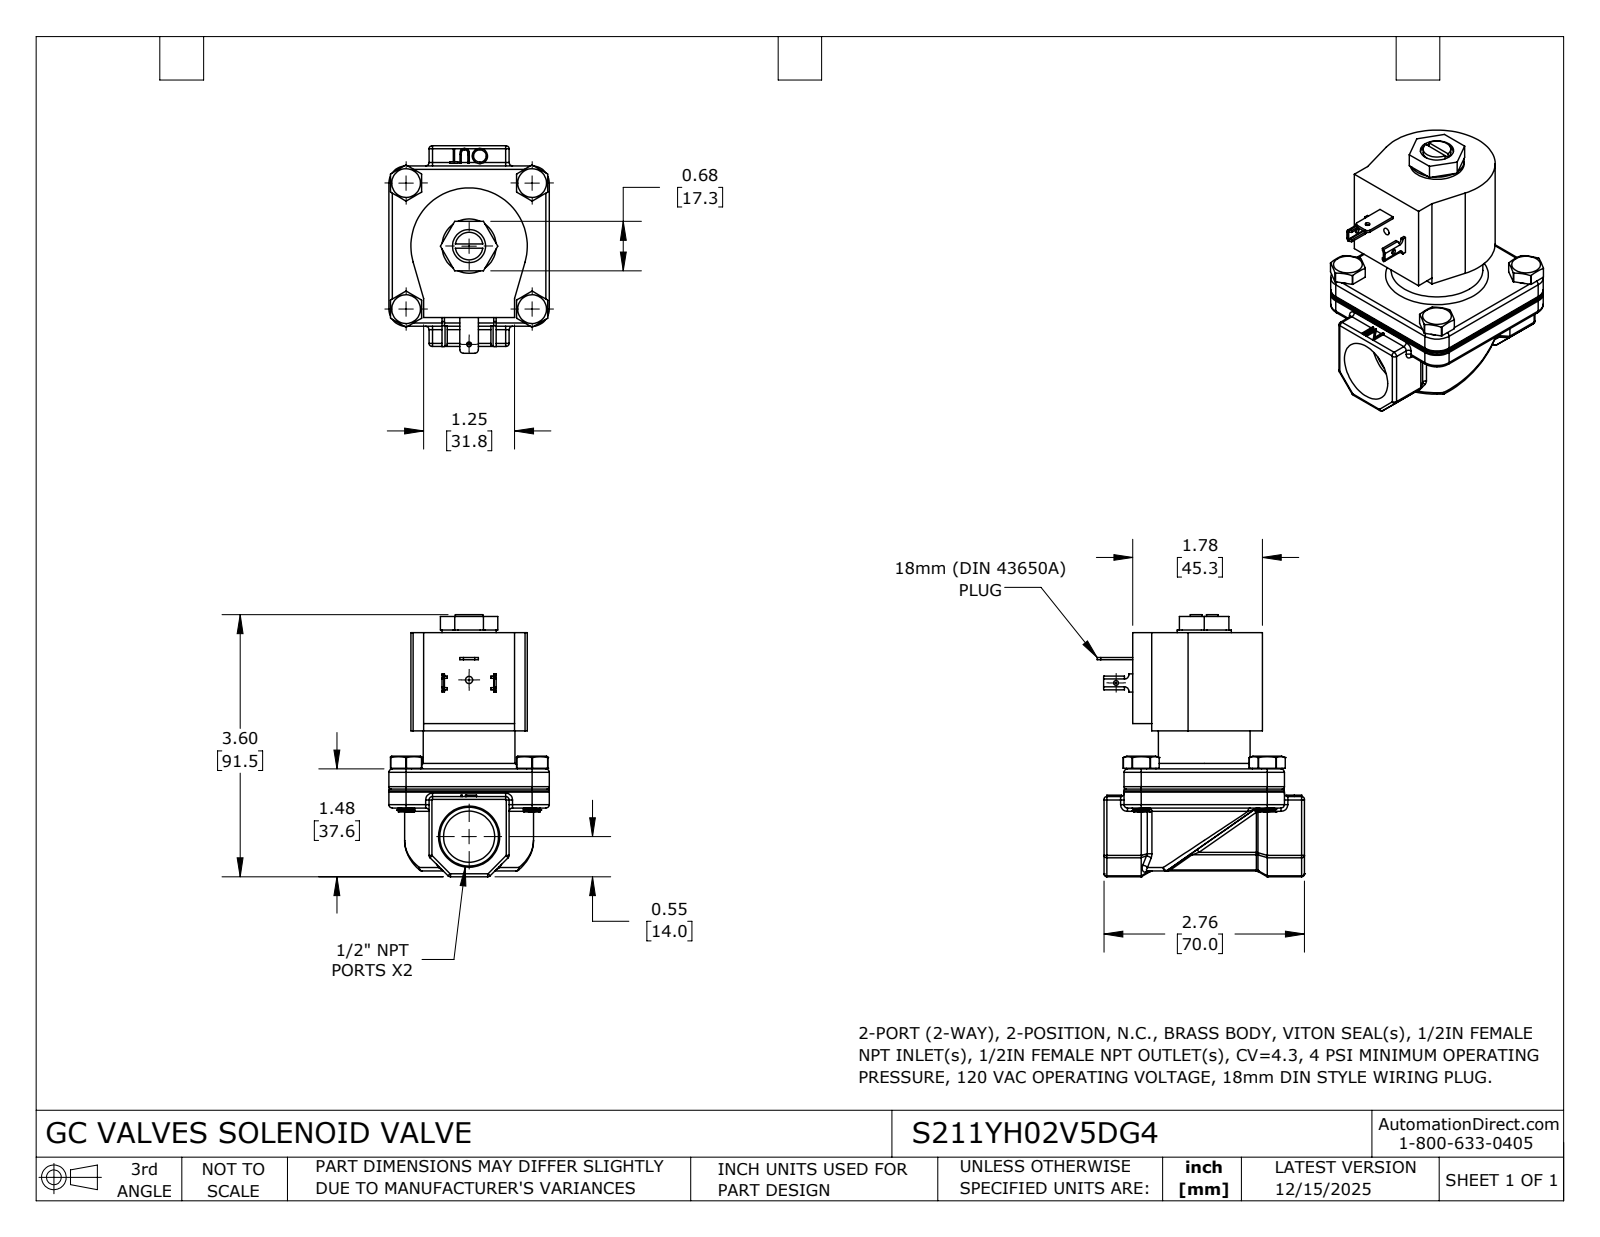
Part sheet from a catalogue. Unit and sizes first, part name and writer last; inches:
Units: inches
Overall size (bounding box): 3.601 × 2.851 × 2.205
Round holes (diameter × count): ⌀0.066 ×1, ⌀0.067 ×1, ⌀0.1 ×1, ⌀0.456 ×1, ⌀0.703 ×1
Round bosses / shafts (diameter × count): ⌀0.407 ×4, ⌀0.242 ×4, ⌀1.26 ×1, ⌀0.746 ×1, ⌀0.38 ×1
Partial cylindrical surfaces — rounded edges, fillets, slot ends (radius × count): R0.047 ×57, R0.04 ×12, R0.006 ×4, R0.031 ×4, R0.041 ×4, R0.234 ×4, R0.236 ×4, R0.05 ×2
Main face-to-face distances: 1.873, 0.551, 1.654, 0.537, 2.41, 2.205, 0.276, 2.48, 1.06, 0.523
Hole centre spacings: 1.35, 2.153
Volume: 8.787 in³ · Surface area: 40.33 in²
Bodies: 1 solid, 521 faces (228 planar, 163 cylindrical, 130 other)
Part name (STEP PRODUCT): S211YH02V5DG4
STEP written by: SolidWorks 2024 (CONFIG_CONTROL_DESIGN)
